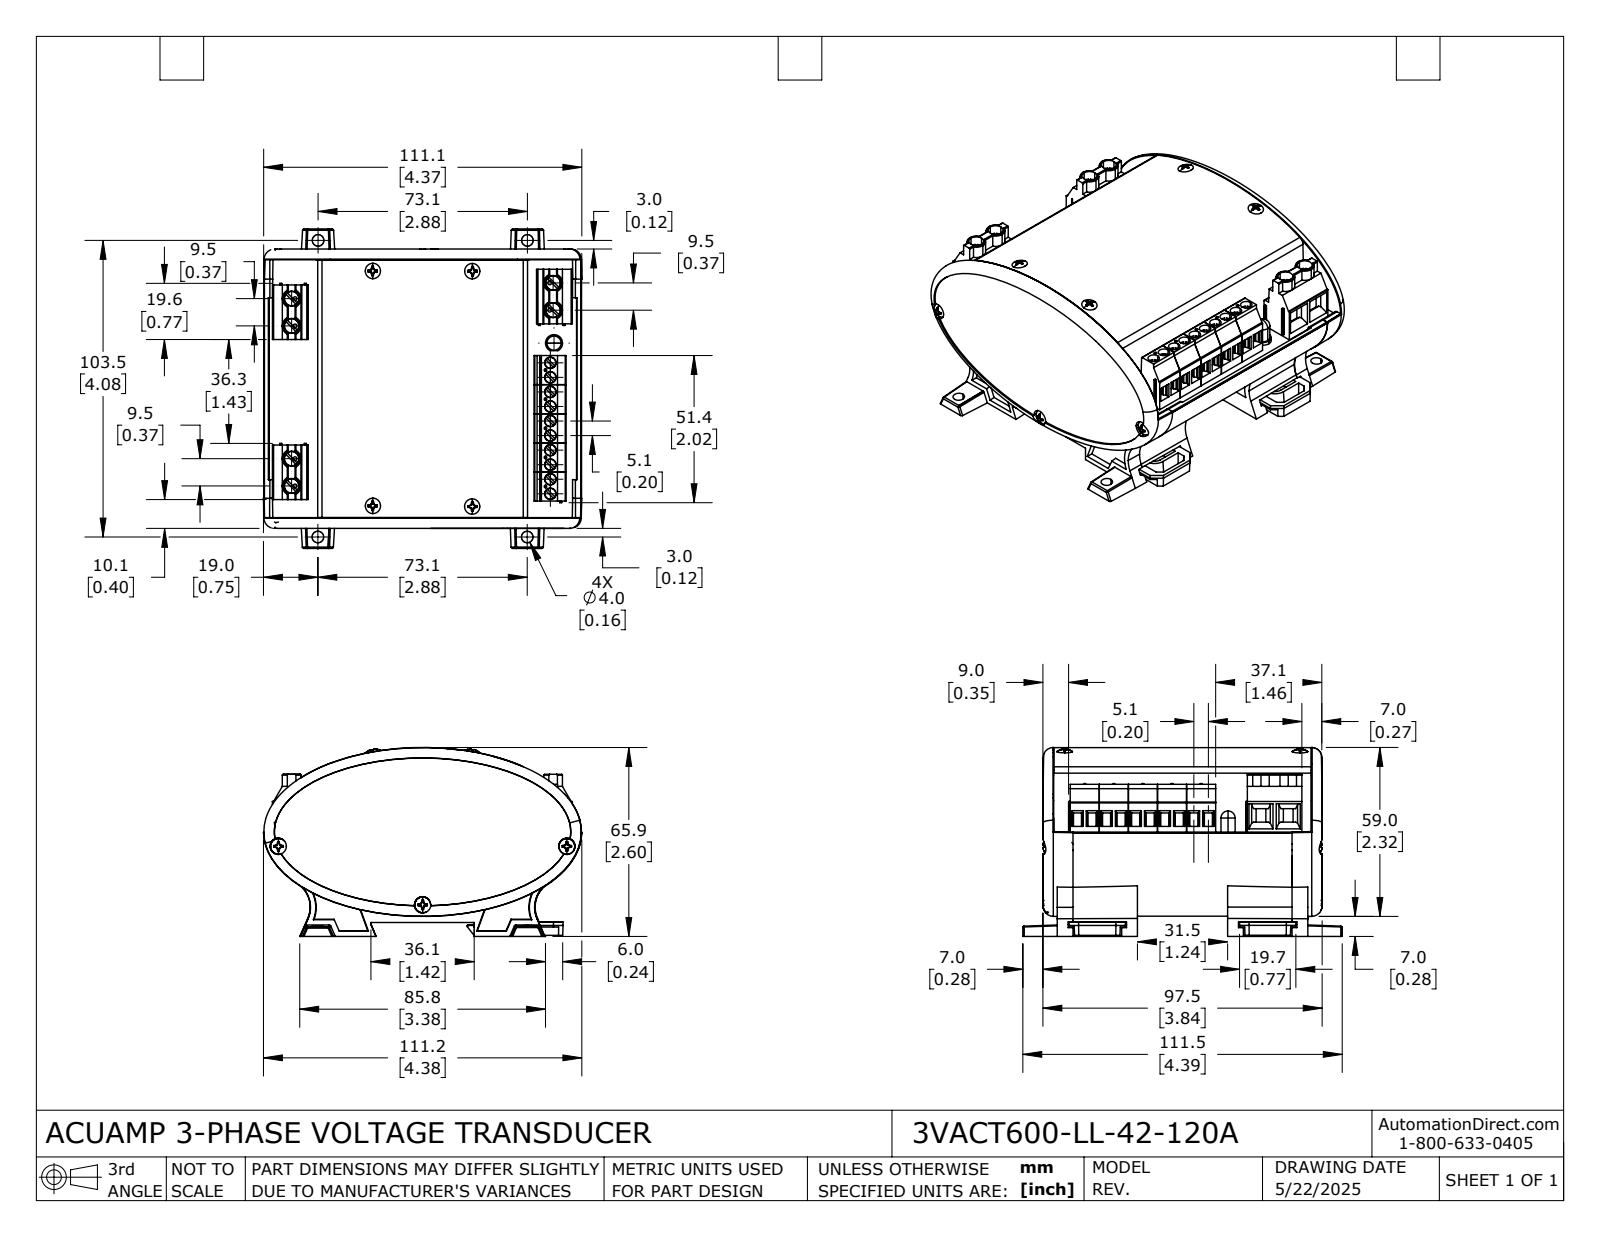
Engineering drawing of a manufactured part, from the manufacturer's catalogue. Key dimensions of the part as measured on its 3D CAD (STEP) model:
Part name (STEP PRODUCT): 3VACT600-LL-42-120A
STEP written by: SolidWorks 2024 (AUTOMOTIVE_DESIGN)
Units: inches
Bodies: 26 solids, 2967 faces (1482 planar, 844 cylindrical, 641 other)
Overall size (bounding box): 7.429 × 4.374 × 2.597
Volume: 11.76 in³ · Surface area: 284.7 in²
Round holes (diameter × count): ⌀0.05 ×12, ⌀0.157 ×10, ⌀0.08 ×6, ⌀0.205 ×6, ⌀0.126 ×4, ⌀0.111 ×3, ⌀0.28 ×3
Round bosses / shafts (diameter × count): ⌀0.051 ×16, ⌀0.15 ×10, ⌀0.112 ×10, ⌀0.067 ×10, ⌀0.197 ×6, ⌀0.018 ×4, ⌀0.234 ×1, ⌀0.194 ×1
Partial cylindrical surfaces — rounded edges, fillets, slot ends (radius × count): R0.006 ×38, R0.039 ×20, R0.02 ×17, R0.008 ×12, R0.012 ×8, R0.01 ×6, R0.128 ×6, R0.018 ×4
Main face-to-face distances: 0.063, 0.128, 6.709, 0.084, 6.838, 6.581, 0.394, 6.444, 0.266, 6.315
Hole centre spacings: 0.2, 0.4, 0.6, 0.8, 1, 1.2, 0.2, 0.2
